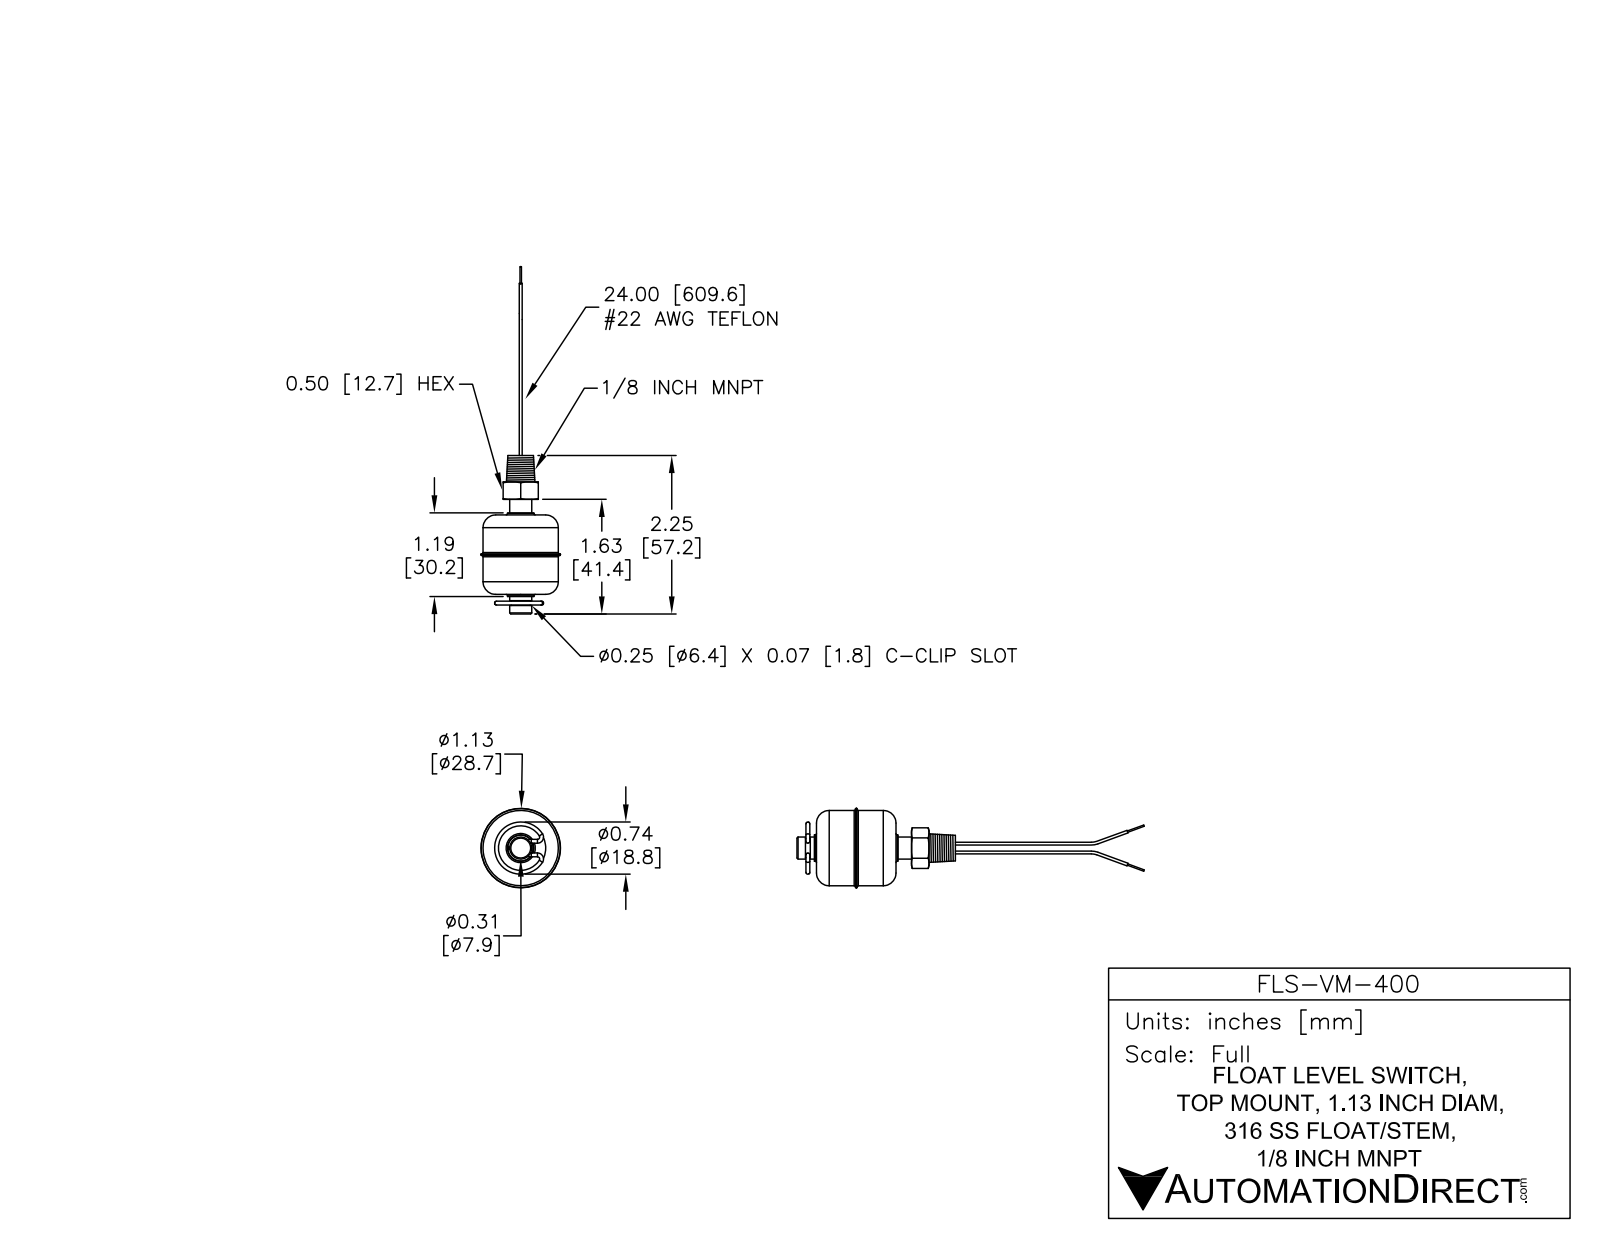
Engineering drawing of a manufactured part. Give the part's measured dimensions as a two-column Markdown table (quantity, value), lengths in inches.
| quantity | value |
| --- | --- |
| part name | FLS-VM-400 |
| STEP written by | SolidWorks 2013 (AUTOMOTIVE_DESIGN) |
| units | inches |
| bodies | 7 solids, 119 faces (31 planar, 38 cylindrical, 50 other) |
| overall size | 4.984 × 1.123 × 1.123 |
| volume | 0.298 in³ |
| surface area | 14.51 in² |
| round holes (diameter × count) | 0.354 × 1, 1.05 × 1 |
| round bosses / shafts (diameter × count) | 0.04 × 4, 0.02 × 2, 1.123 × 1, 1.07 × 1, 0.374 × 1, 0.313 × 1, 0.313 × 1, 0.25 × 1 |
| main face-to-face distances | 1.119, 1.129, 1.109, 1.344, 1.335, 0.226, 0.216, 0.25, 1.594, 1.585 |
